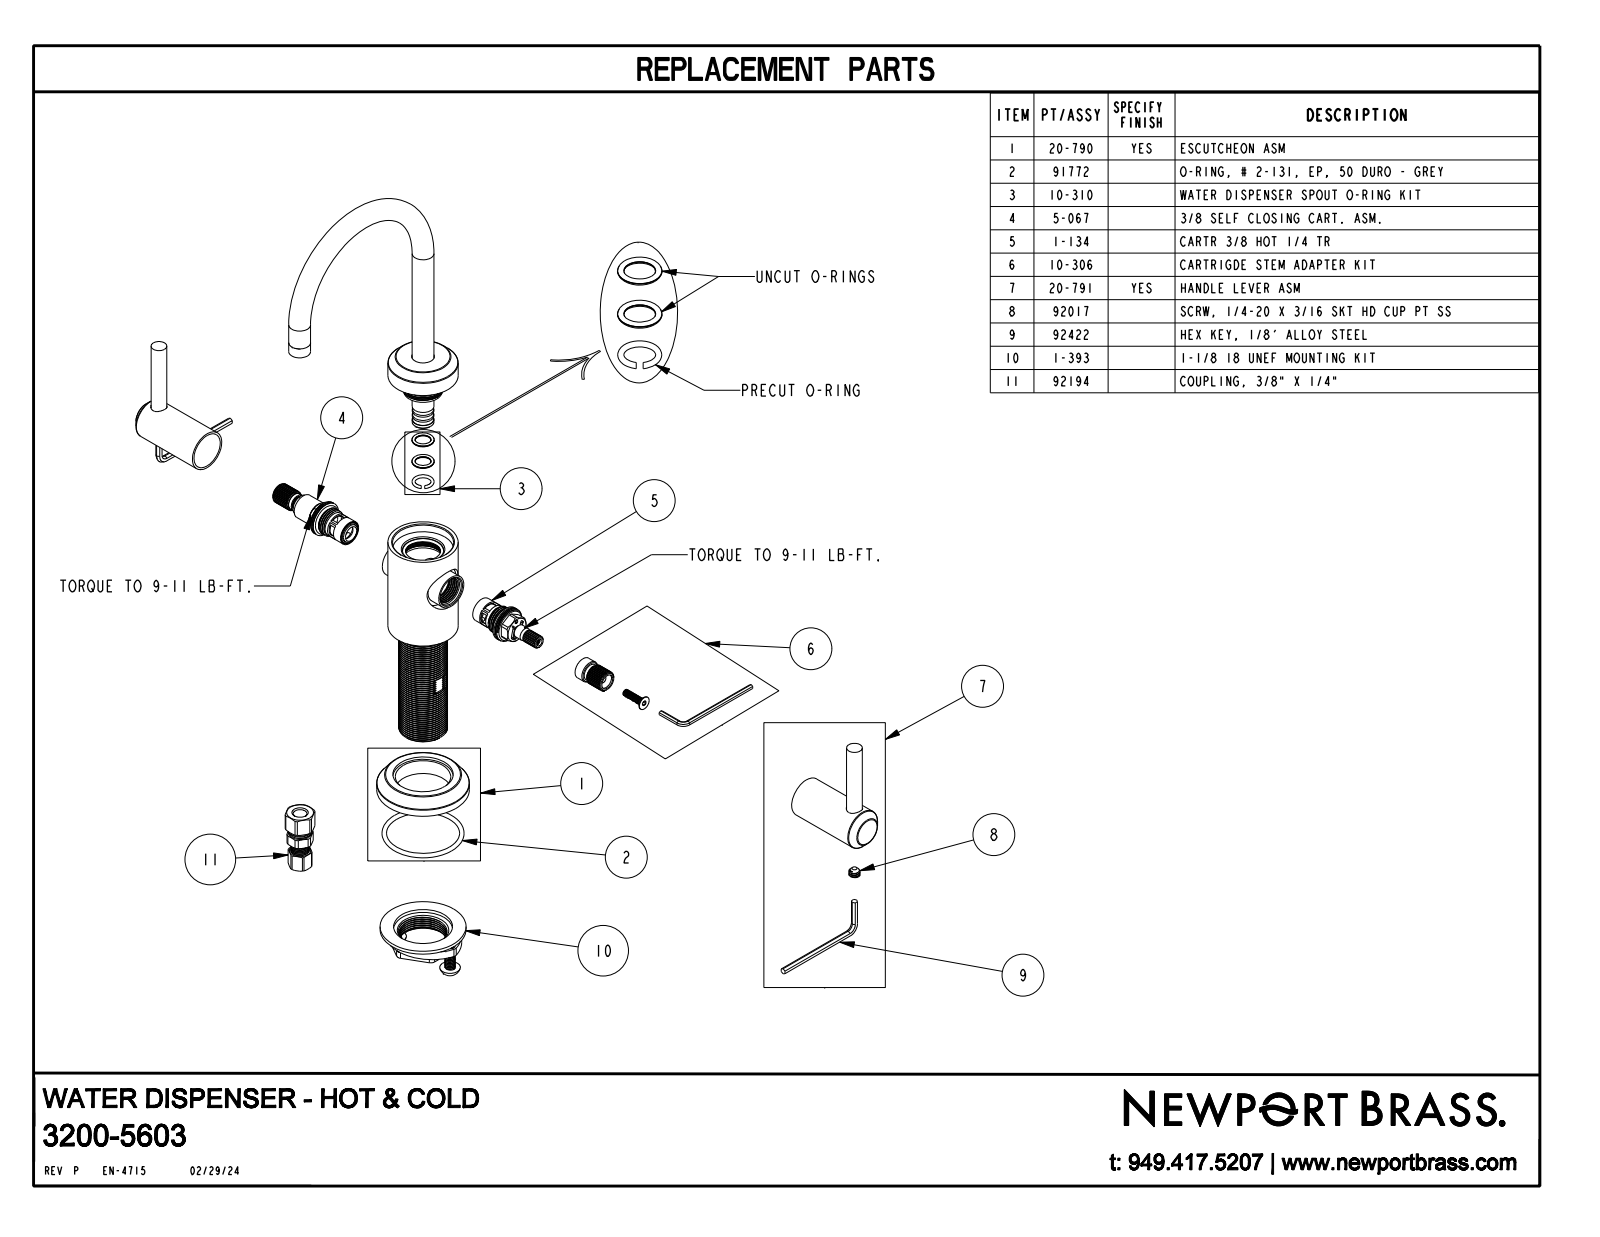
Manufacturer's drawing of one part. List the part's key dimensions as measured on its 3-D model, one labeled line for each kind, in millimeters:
Part name (STEP PRODUCT): 3200-5603
STEP written by: CREO PARAMETRIC BY PTC INC, 2018400 (CONFIG_CONTROL_DESIGN)
Units: millimetres
Bodies: 1 solid, 62 faces (12 planar, 24 cylindrical, 26 other)
Overall size (bounding box): 235.6 × 135 × 132.6
Volume: 198 400 mm³ · Surface area: 36 360 mm²
Round holes (diameter × count): ⌀9.5 ×2, ⌀25.4 ×1
Round bosses / shafts (diameter × count): ⌀12.7 ×2, ⌀9.1 ×2, ⌀54 ×1, ⌀40.9 ×1, ⌀24.1 ×1
Main face-to-face distances: 84, 132.6, 10.8, 73.2, 104.6, 93.8, 20.6, 165.7, 154.9, 81.8
Hole centre spacings: 111.4
